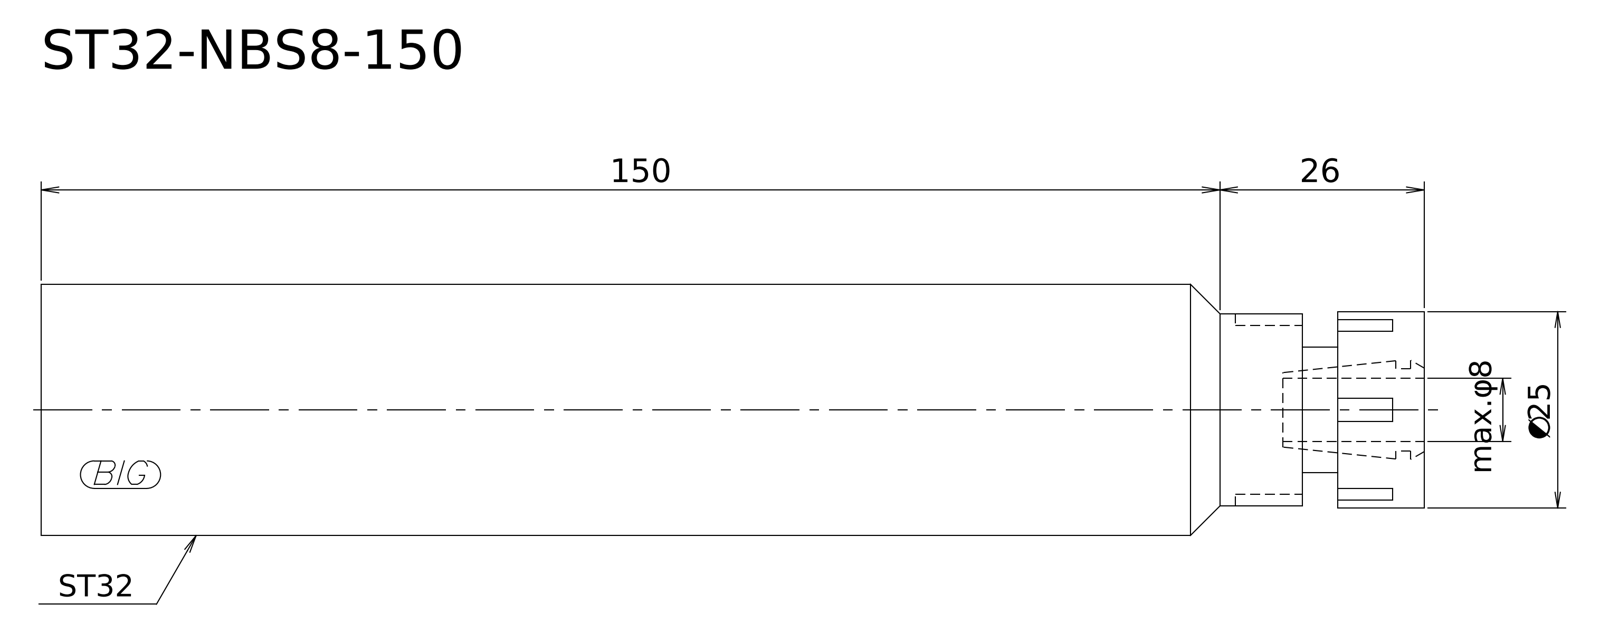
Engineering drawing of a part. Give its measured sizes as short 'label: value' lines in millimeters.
written by: Kubotek KeyCreator V8.5.1 (14335) (CONFIG_CONTROL_DESIGN)
unit: mm
bodies: 1 solid, 9 faces (4 planar, 4 cylindrical, 1 other)
size: 176 × 32 × 32
volume: 131 240 mm³; area: 18 927 mm²
bosses: 1× ⌀32, 1× ⌀25, 1× ⌀24.5, 1× ⌀16
face distances: 176, 11, 165, 15.5, 4.5, 160.5
